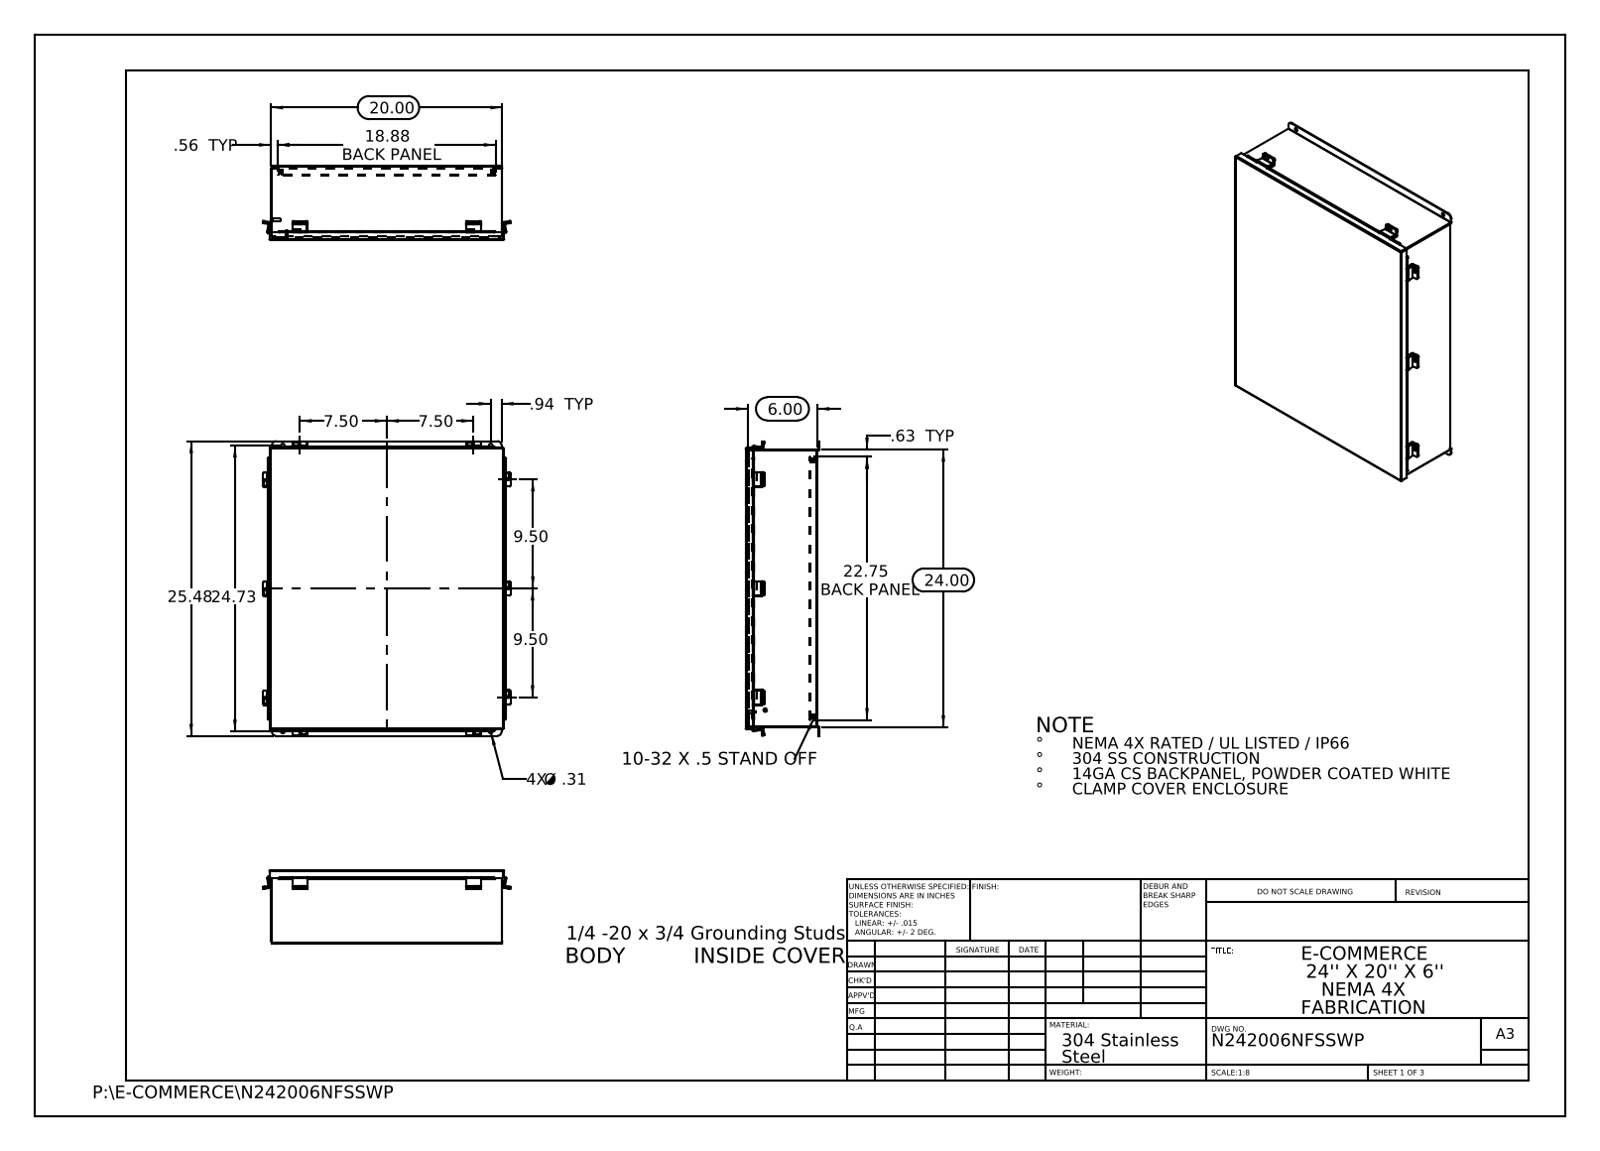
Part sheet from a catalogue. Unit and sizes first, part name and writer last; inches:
Units: inches
Overall size (bounding box): 25.476 × 21.407 × 6.39
Round holes (diameter × count): ⌀0.25 ×14, ⌀0.187 ×4, ⌀0.312 ×4
Round bosses / shafts (diameter × count): ⌀0.313 ×4, ⌀0.315 ×2, ⌀0.236 ×2
Partial cylindrical surfaces — rounded edges, fillets, slot ends (radius × count): R0.125 ×35, R0.133 ×20, R0.009 ×16, R0.013 ×12, R0.088 ×12, R0.083 ×8, R0.1 ×8, R0.084 ×4
Main face-to-face distances: 0.075, 6.128, 6.053, 6.203, 0.074, 5.628, 0.575, 0.5, 5.553, 0.649
Hole centre spacings: 1.315, 9.425, 18.222, 23.427, 29.65, 15, 17.976, 18.375
Volume: 155.6 in³ · Surface area: 4 197 in²
Bodies: 31 solids, 732 faces (484 planar, 228 cylindrical, 20 other)
Part name (STEP PRODUCT): N242006NFSSWP JIC Clamp Bracket; N242006NFSSWP; N242006NFSSWP JIC_Standoff; N242006NFSSWP HW-CD-S-25020-034 (+6 more)
STEP written by: SolidWorks 2013 (CONFIG_CONTROL_DESIGN)
